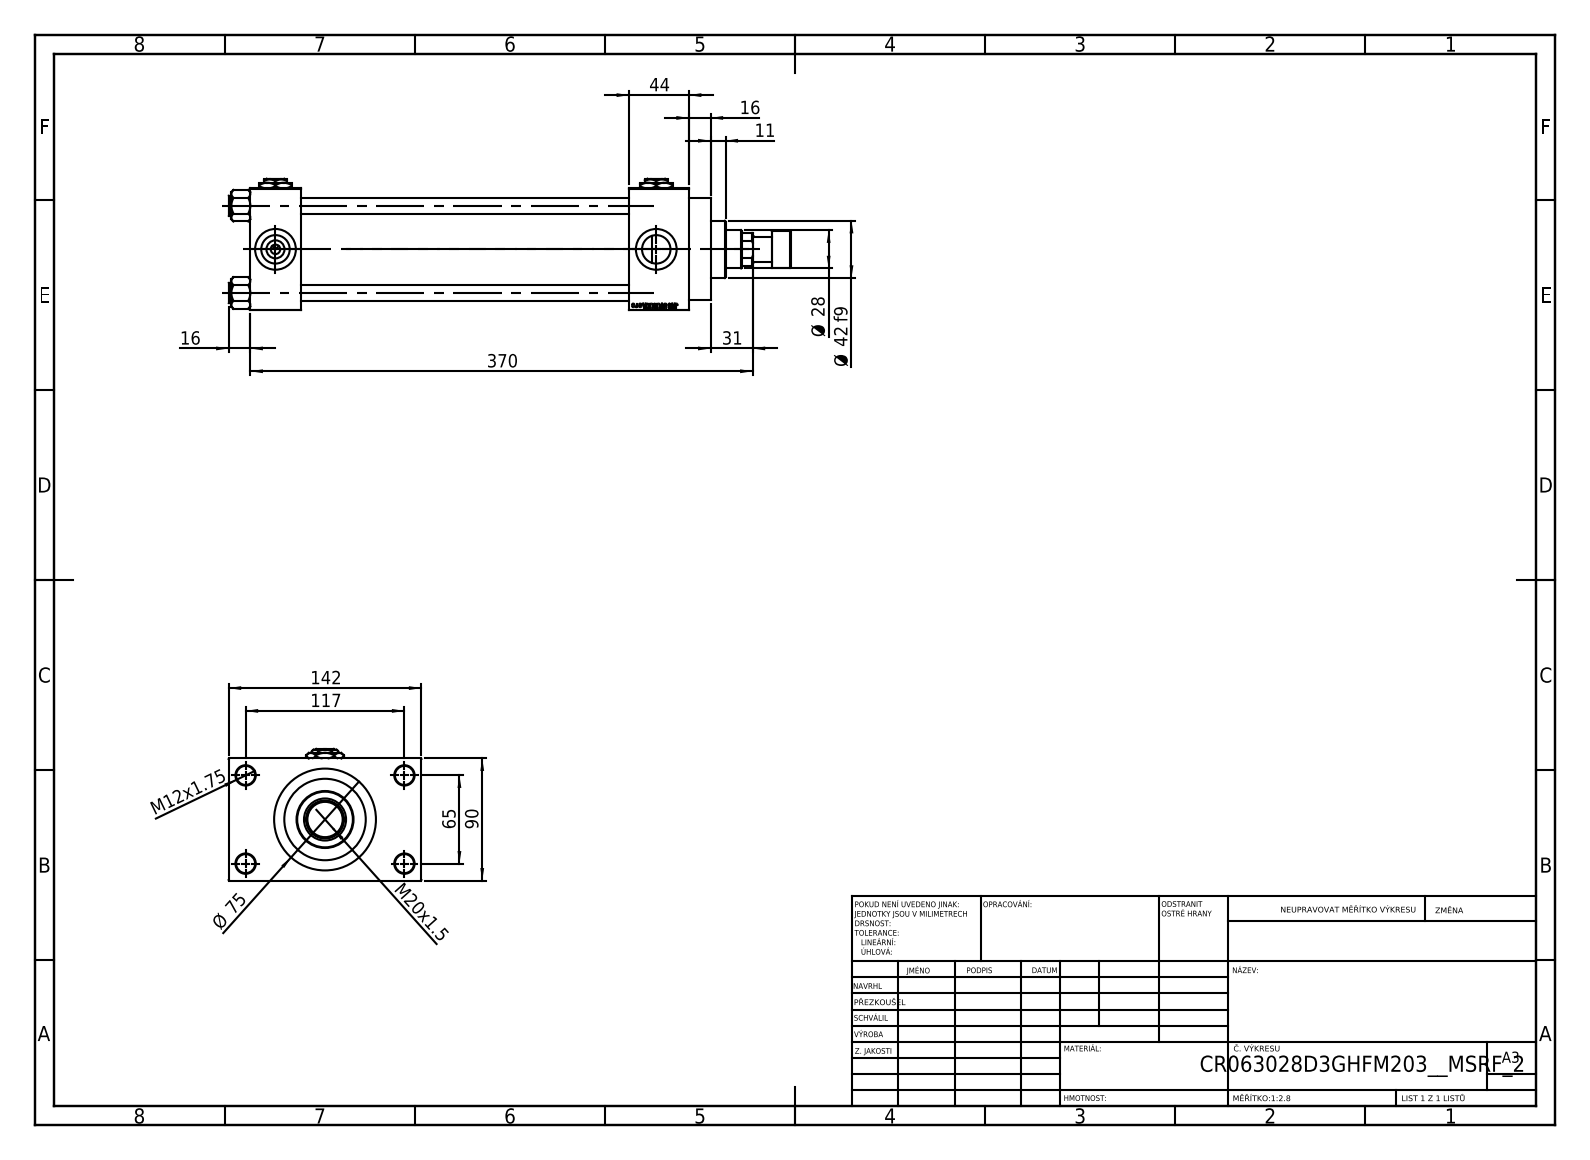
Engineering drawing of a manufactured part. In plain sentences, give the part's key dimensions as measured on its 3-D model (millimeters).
The part is named "NUT_M5_D; V215CR_ROD_END_F; V215CR_D_Body; Zatka_pro_OIL_PORT (+3 more)". Its 3-D file was written by "SolidWorks 2019 (CONFIG_CONTROL_DESIGN)". It is 14 solids with 1218 faces: 549 planar, 103 cylindrical and 566 other. Overall it measures 414 by 142 by 97 millimeters. Its volume is 1 412 000 cubic millimeters and its surface area 327 780 square millimeters. Round holes: 4 of diameter 12, 4 of diameter 14, 4 of diameter 20.96, 4 of diameter 30, 3 of diameter 7, 1 of diameter 18.5, 1 of diameter 28, 1 of diameter 31, 1 of diameter 50, 1 of diameter 60, 1 of diameter 63. Round bosses or shafts: 4 of diameter 15, 1 of diameter 75, 1 of diameter 69, 1 of diameter 42, 1 of diameter 27, 1 of diameter 18. The main face-to-face distances are 90, 242, 37, 279, 286, 323, 44, 26, 116, 16. The hole center spacings are 26.35, 45.47, 64.3, 66.92, 69.81, 90.65, 111.34, 65.
